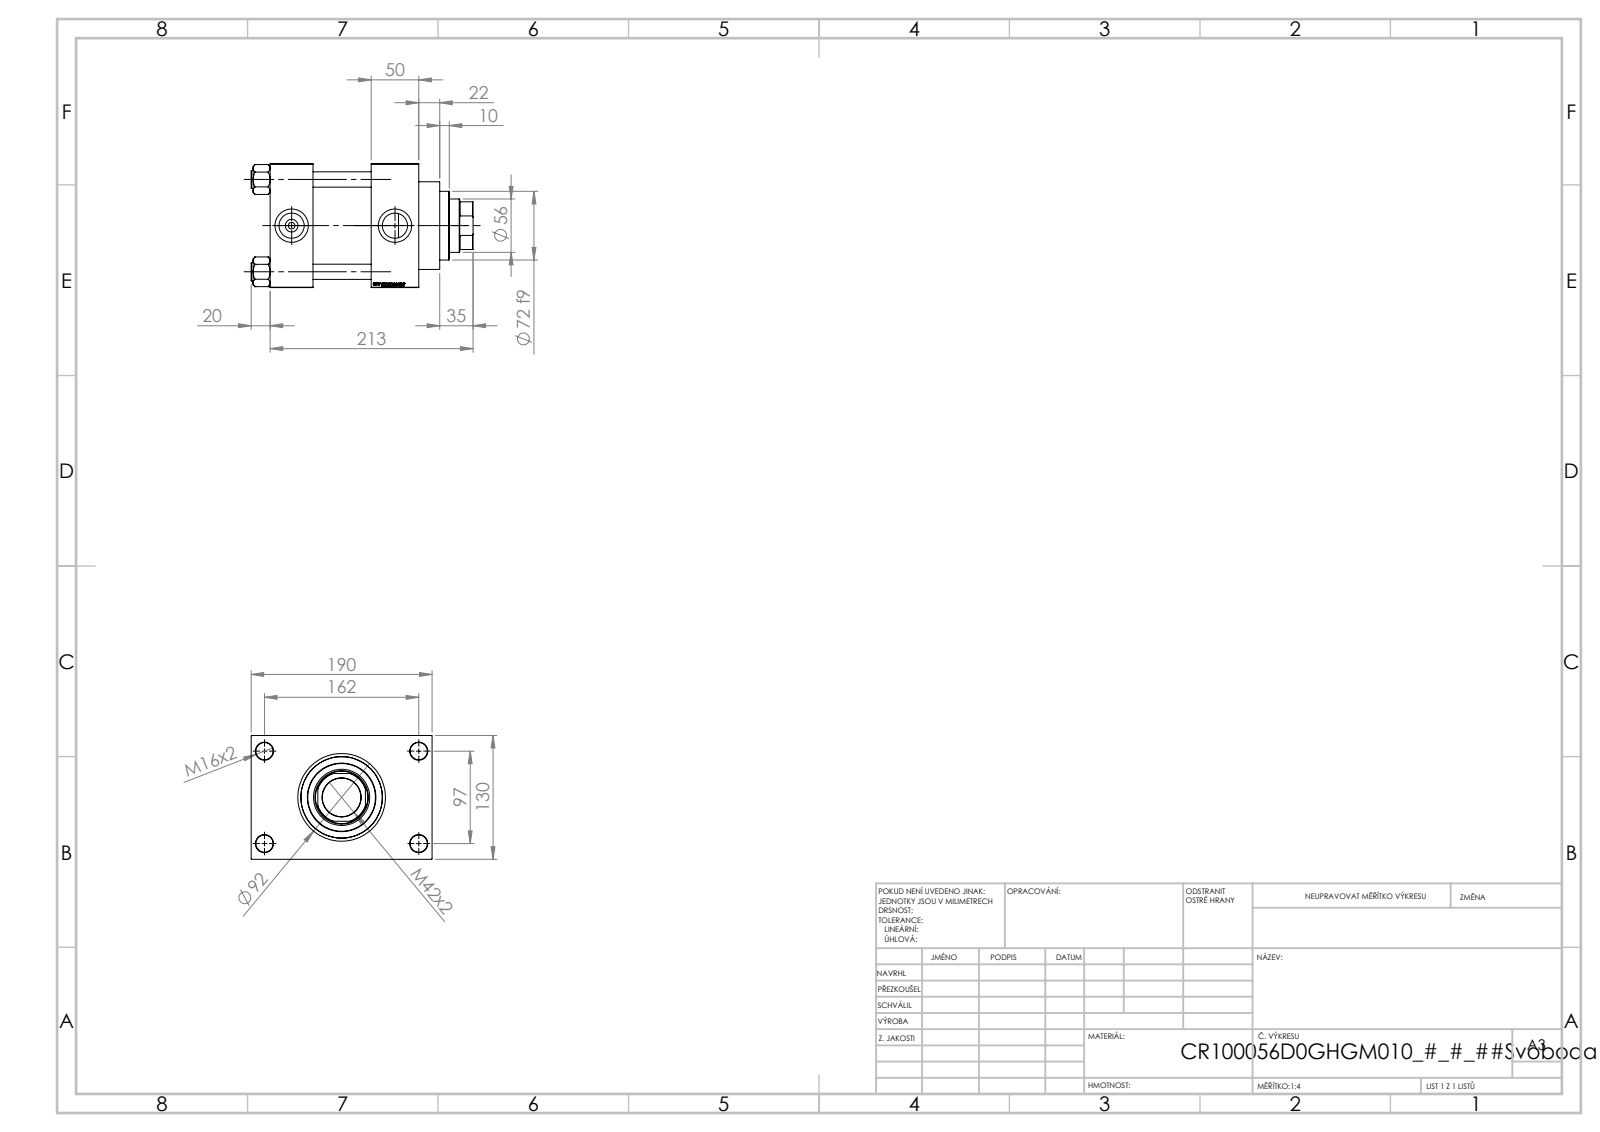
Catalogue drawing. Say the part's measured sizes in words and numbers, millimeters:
The part is named "V215_VC_A; NUT_M5_D; V215CR_D_Body; V215CR_VCP_D (+1 more)". Its 3-D file was written by "SolidWorks 2019 (CONFIG_CONTROL_DESIGN)". It is 11 solids with 1151 faces: 545 planar, 88 cylindrical and 518 other. Overall it measures 233 by 190 by 130 millimeters. Its volume is 2 586 000 cubic millimeters and its surface area 352 122 square millimeters. Round holes: 4 of diameter 16, 4 of diameter 18, 2 of diameter 7, 2 of diameter 26.44, 2 of diameter 35, 1 of diameter 40.5, 1 of diameter 56, 1 of diameter 59, 1 of diameter 76, 1 of diameter 85.5, 1 of diameter 100. Round bosses or shafts: 4 of diameter 19, 1 of diameter 106, 1 of diameter 92, 1 of diameter 72. Partial cylindrical surfaces (rounded edges, fillets, slot ends): 1 of radius 27. The main face-to-face distances are 130, 50, 45, 106, 61, 156, 111, 30, 160, 10. The hole center spacings are 32.55, 68.52, 94.41, 96.9, 102.27, 129.45, 161.73, 97.
